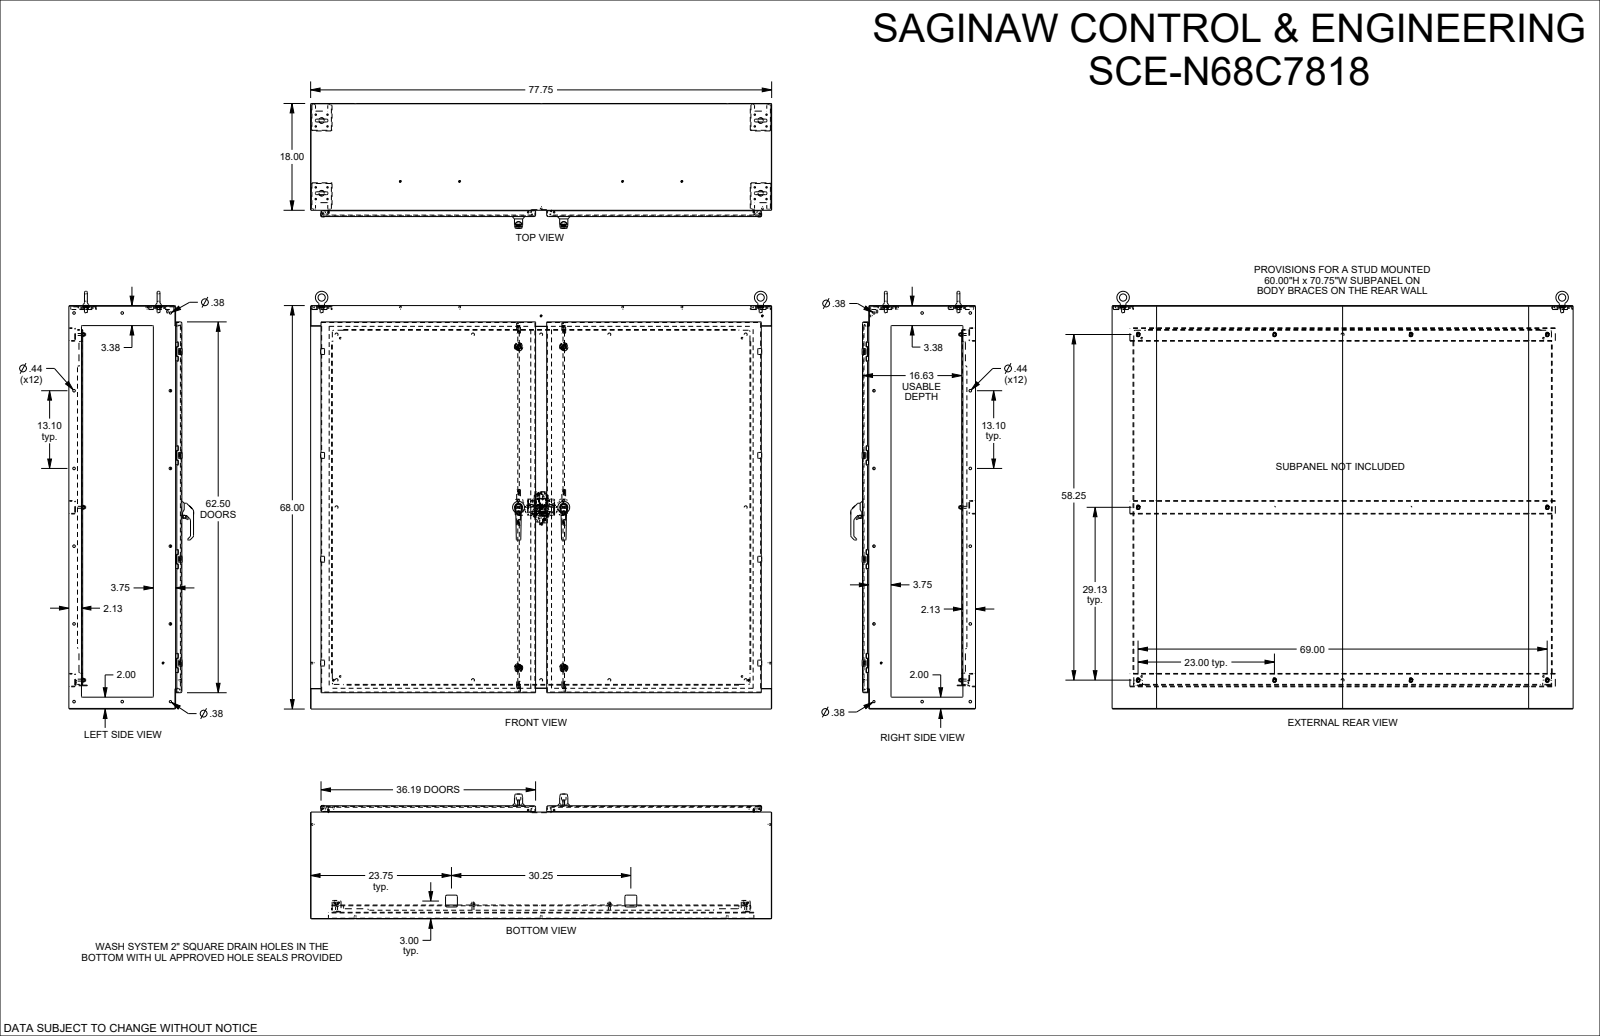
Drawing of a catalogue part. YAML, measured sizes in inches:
part_name: "SCE-N68C7818_REV2"
step_written_by: "SolidWorks 2023 (AUTOMOTIVE_DESIGN)"
units: inches
bodies: {solids: 60, faces: 8179, planar: 3290, cylindrical: 2690, other: 2199}
overall_size: [77.75, 70.423, 21.046]
volume: 1724
surface_area: 32693
round_holes:
  - {diameter: 0.25, count: 20}
  - {diameter: 0.375, count: 18}
  - {diameter: 0.205, count: 16}
  - {diameter: 0.244, count: 16}
  - {diameter: 0.437, count: 12}
  - {diameter: 0.04, count: 8}
  - {diameter: 0.17, count: 8}
  - {diameter: 0.218, count: 8}
  - {diameter: 0.256, count: 4}
  - {diameter: 0.343, count: 4}
  - {diameter: 0.344, count: 4}
  - {diameter: 0.36, count: 4}
round_bosses_or_shafts:
  - {diameter: 0.17, count: 24}
  - {diameter: 0.25, count: 20}
  - {diameter: 0.24, count: 16}
  - {diameter: 0.196, count: 10}
  - {diameter: 1.4, count: 4}
  - {diameter: 1, count: 4}
  - {diameter: 0.73, count: 4}
  - {diameter: 0.341, count: 4}
partial_cylinders:
  - {radius: 0.03, count: 228}
  - {radius: 0.015, count: 162}
  - {radius: 0.02, count: 128}
  - {radius: 0.125, count: 100}
  - {radius: 0.005, count: 50}
  - {radius: 0.062, count: 50}
  - {radius: 0.02, count: 48}
  - {radius: 0.25, count: 46}
face_to_face_distances: [0.104, 18.954, 19.057, 18.85, 67.896, 17.896, 1.058, 68, 67.792, 18]
hole_center_spacings: [17.5, 35, 1.979, 72.868, 13.1, 20.873, 74.825, 74.9]
